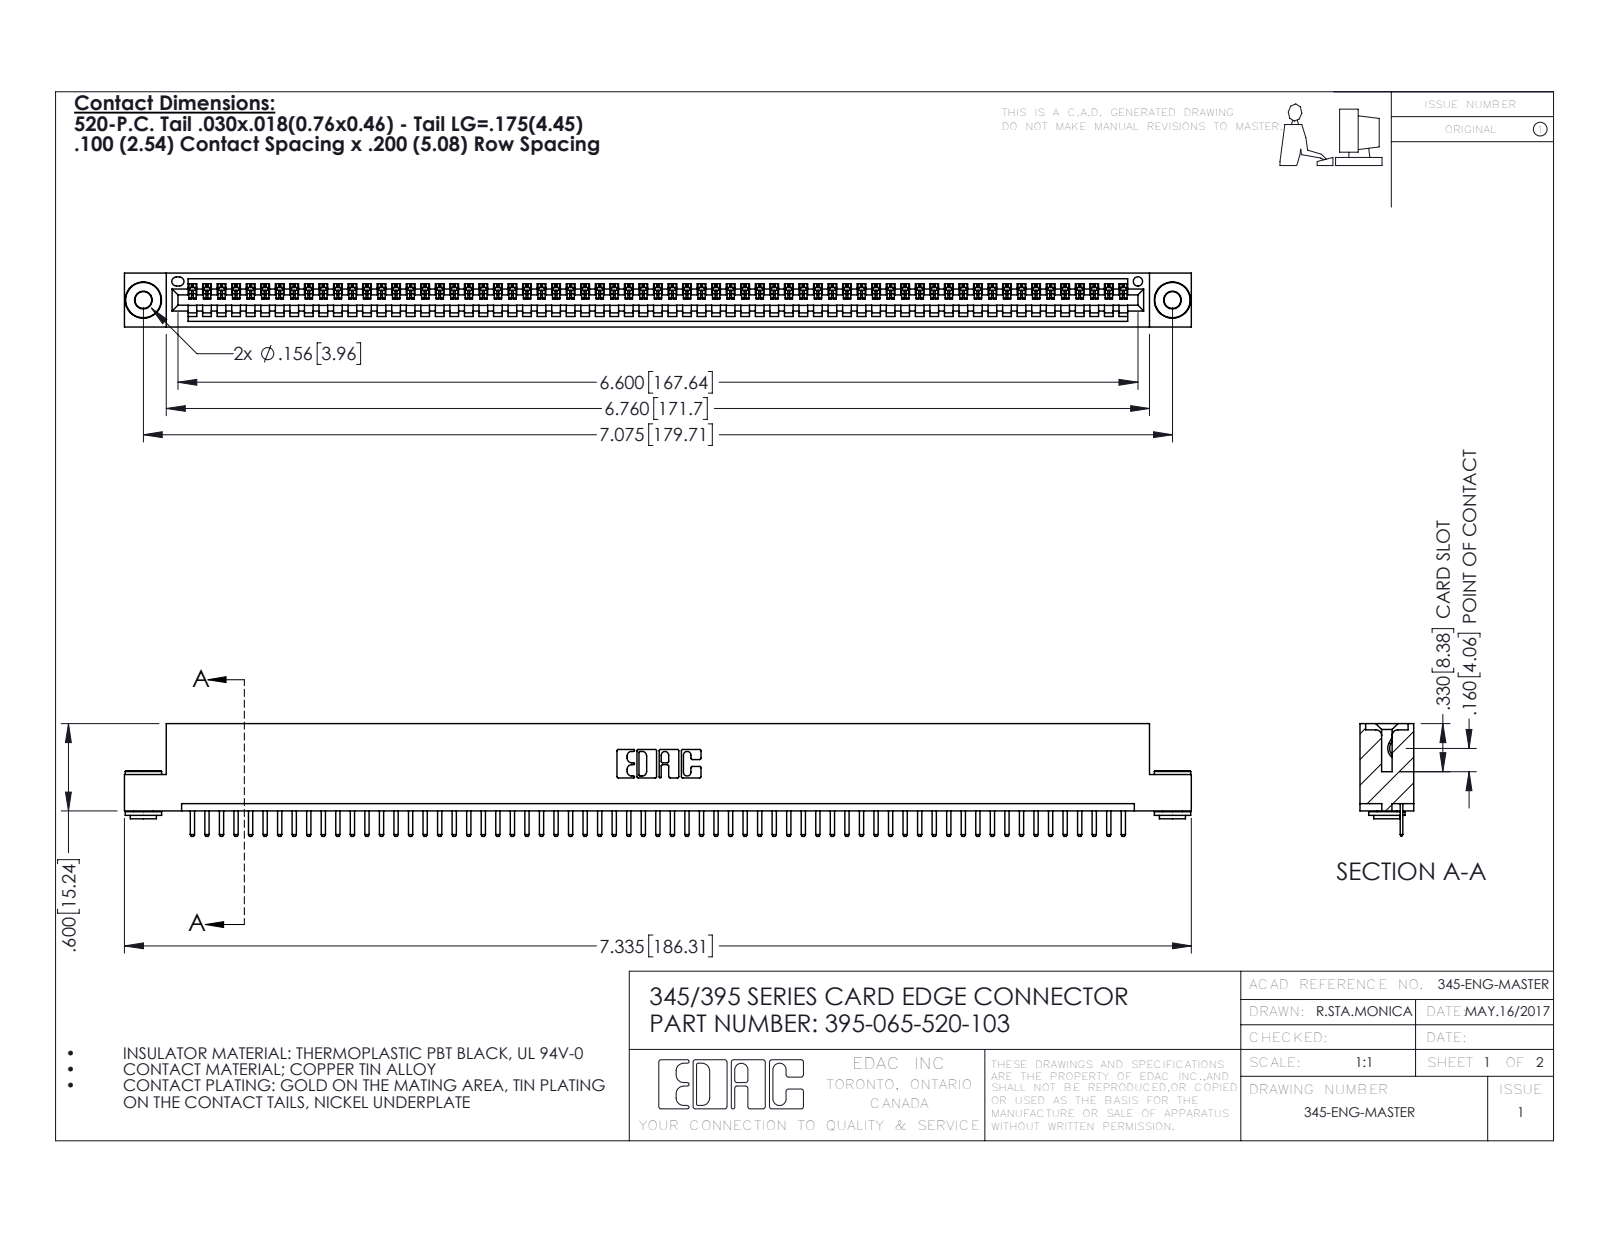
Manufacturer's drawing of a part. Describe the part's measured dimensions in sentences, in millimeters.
The part is named "345-250-002_345-250-002-102; 345-292-001_345-293-120; 345 Part_Flush Mounting Lugs - 0.156 Dia-TH; 395-065-520-103". Its 3-D file was written by "SolidWorks 2016 (CONFIG_CONTROL_DESIGN)". It is 68 solids with 4194 faces: 2820 planar, 1366 cylindrical and 8 other. Overall it measures 186.3 by 19.7 by 9.4 millimeters. Its volume is 17 710 cubic millimeters and its surface area 23 460 square millimeters. Round holes: 2 of diameter 2.9, 2 of diameter 4, 1 of diameter 1.6. Round bosses or shafts: 2 of diameter 6.4, 2 of diameter 4.6, 2 of diameter 3.5. Partial cylindrical surfaces (rounded edges, fillets, slot ends): 132 of radius 0.3, 130 of radius 0.2, 22 of radius 0.3, 6 of radius 0.2, 6 of radius 0.8, 3 of radius 0.7, 2 of radius 0.8, 2 of radius 1. The main face-to-face distances are 1.8, 7.6, 9.4, 5.1, 0.6, 2.5, 6.9, 5.7, 1.8, 3.8. The hole center spacings are 6.9, 173.7, 179.7.
